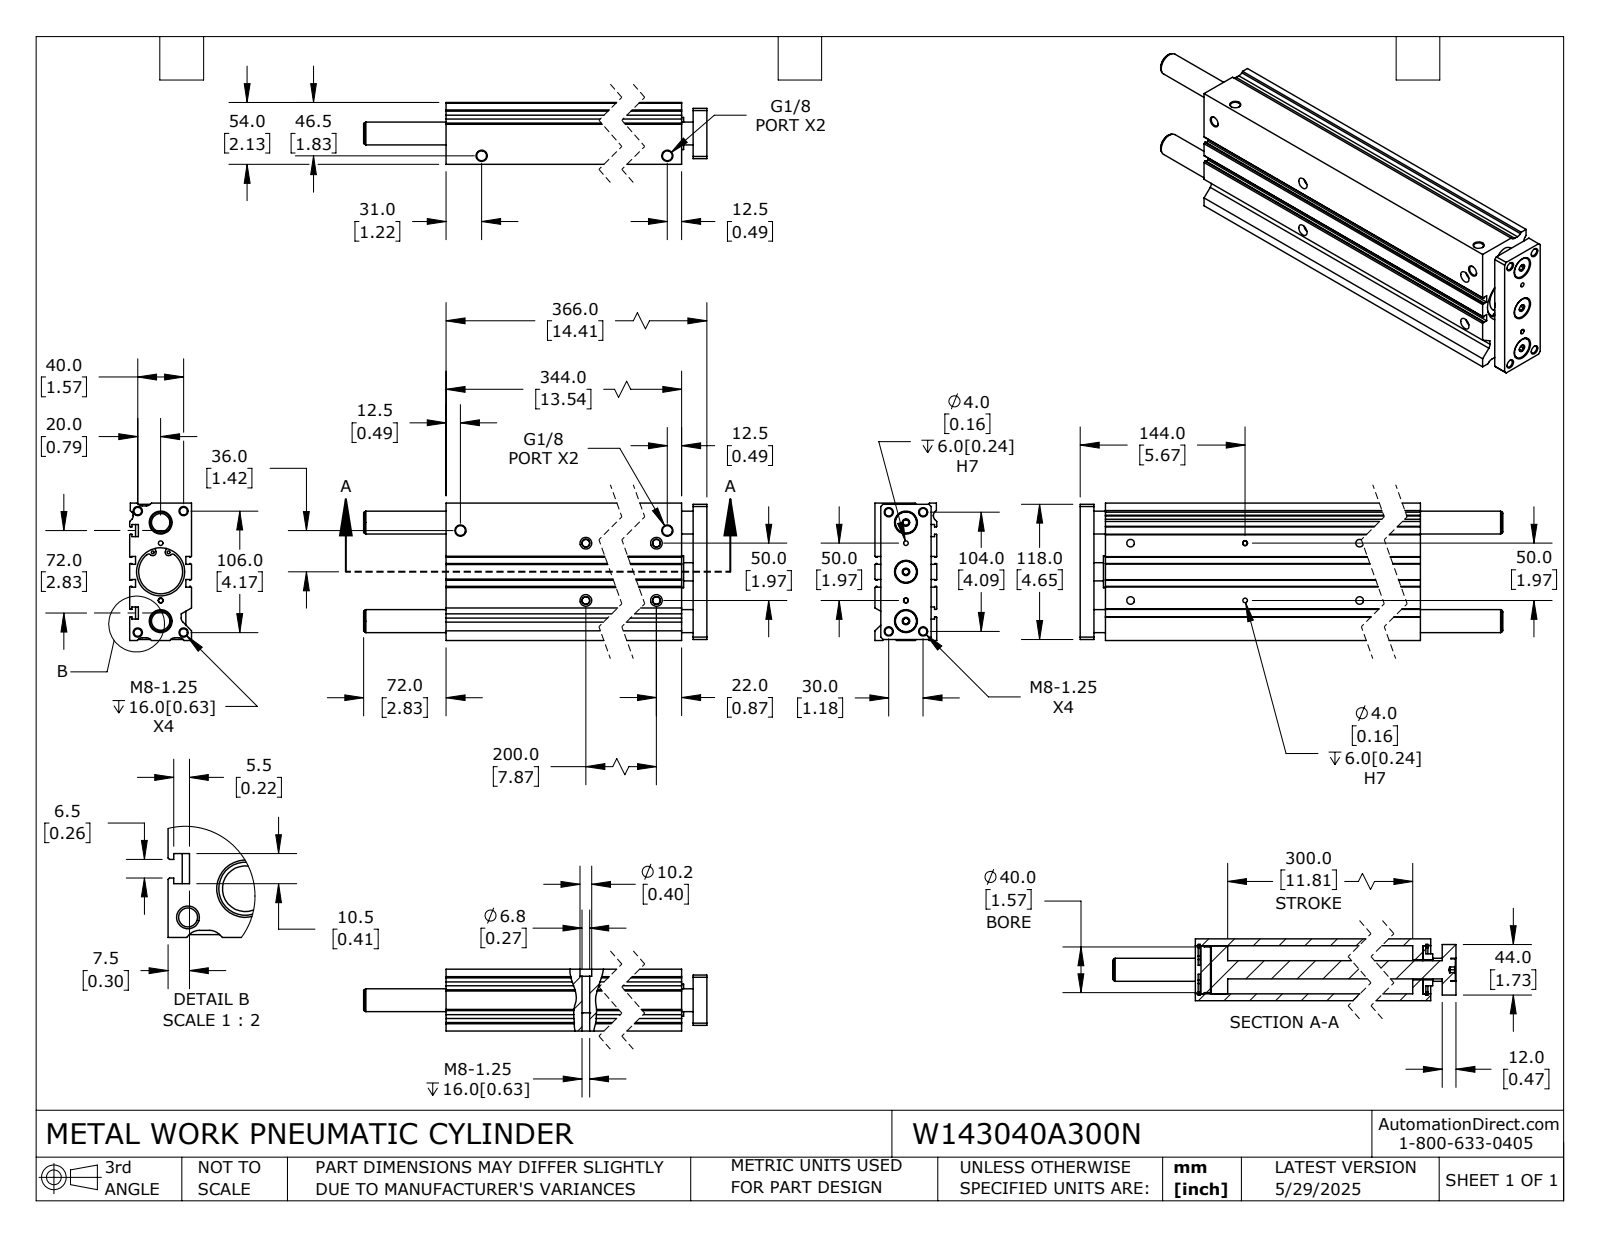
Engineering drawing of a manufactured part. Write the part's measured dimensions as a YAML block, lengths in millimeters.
part_name: "W143040A300N_BODY; W143040A300N; W143040A300N_ROD"
step_written_by: "SolidWorks 2024 (CONFIG_CONTROL_DESIGN)"
units: millimeters
bodies: {solids: 6, faces: 393, planar: 192, cylindrical: 151, other: 50}
overall_size: [438, 120, 54]
volume: 1799000
surface_area: 363100
round_holes:
  - {diameter: 6.7, count: 12}
  - {diameter: 2.5, count: 4}
  - {diameter: 4, count: 4}
  - {diameter: 6.8, count: 4}
  - {diameter: 8.6, count: 4}
  - {diameter: 10.2, count: 4}
  - {diameter: 5, count: 3}
  - {diameter: 20, count: 3}
  - {diameter: 17.7, count: 1}
  - {diameter: 38.4, count: 1}
round_bosses_or_shafts:
  - {diameter: 19, count: 3}
  - {diameter: 44.5, count: 2}
  - {diameter: 42, count: 1}
  - {diameter: 40, count: 1}
  - {diameter: 28, count: 1}
  - {diameter: 16, count: 1}
partial_cylinders:
  - {radius: 5, count: 7}
  - {radius: 2, count: 4}
  - {radius: 2.3, count: 4}
  - {radius: 2.9, count: 4}
  - {radius: 4, count: 2}
face_to_face_distances: [54, 5, 49, 2.5, 120, 7.5, 46.5, 41.5, 44, 72]
hole_center_spacings: [5.1, 10.5, 17.5, 18.3, 22.4, 26.9, 30.9, 34.4]
